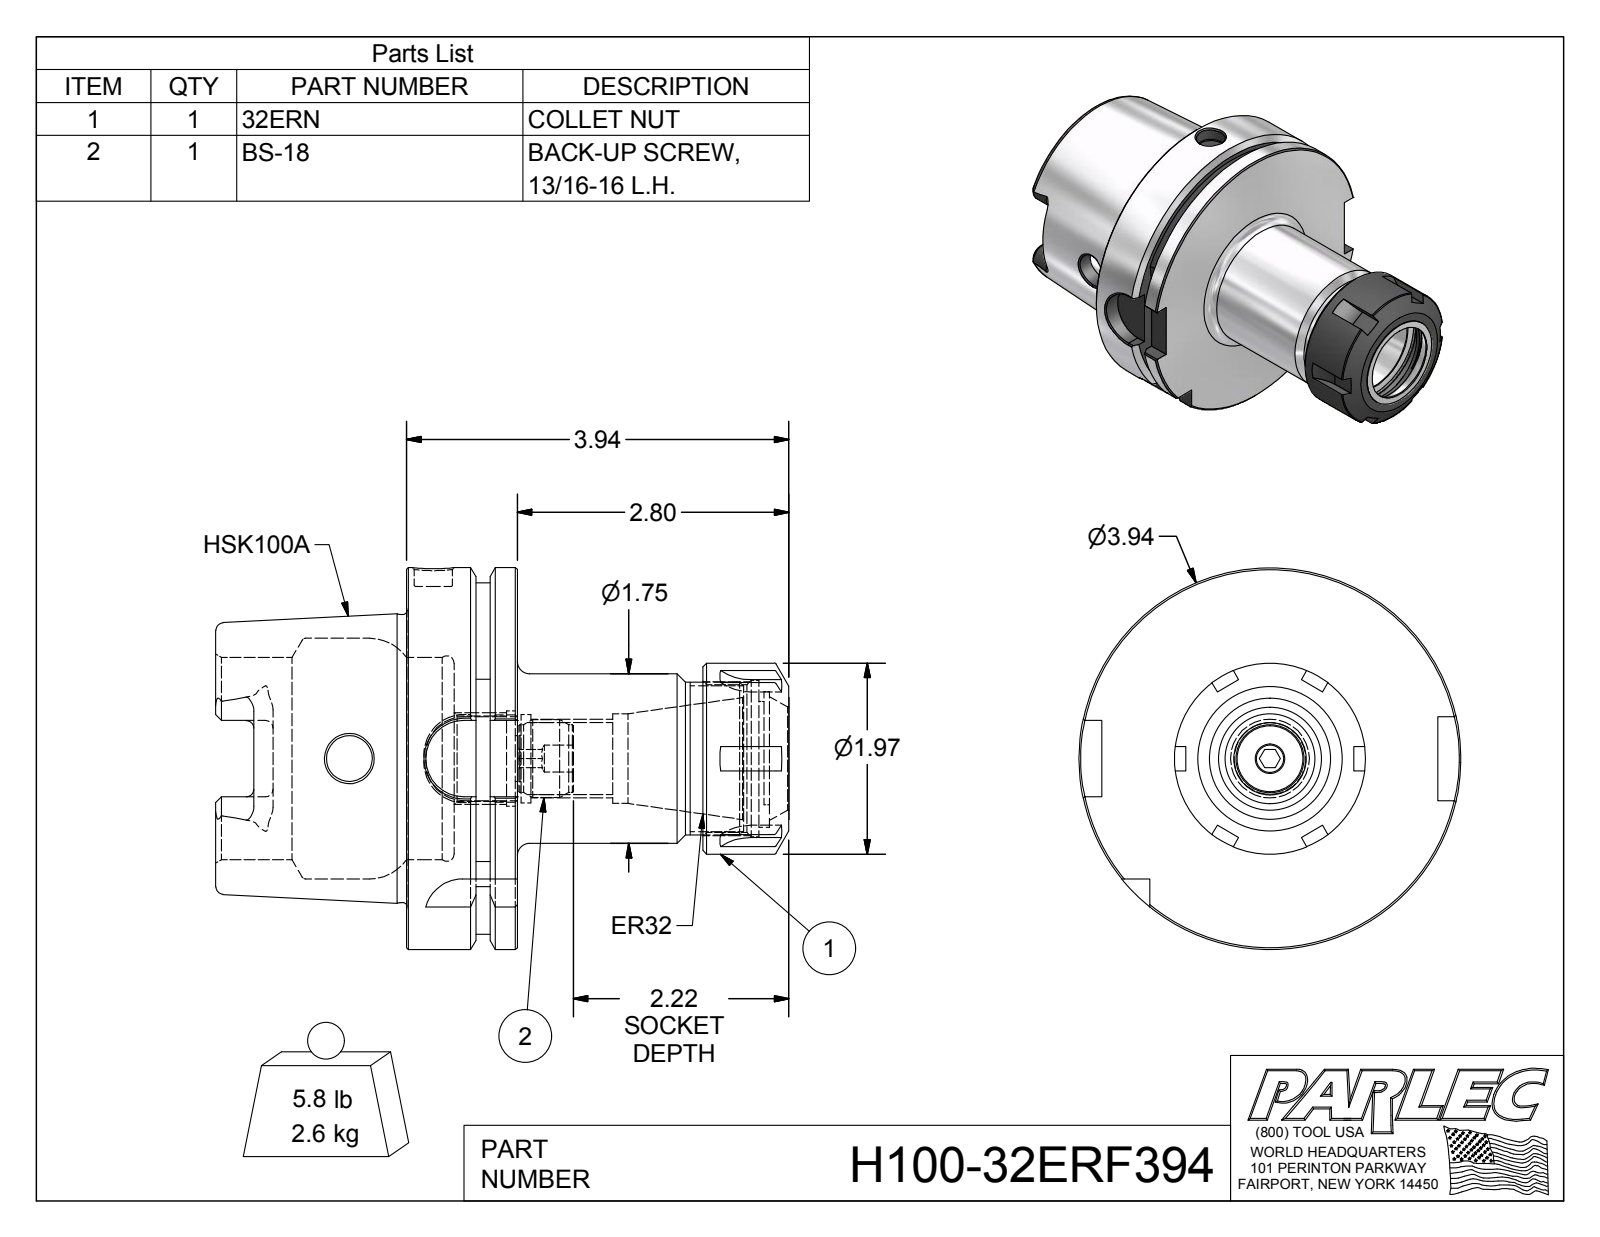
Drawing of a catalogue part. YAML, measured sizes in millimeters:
part_name: "H100-32ER4-1; 32ERN; BS-18; H100-32ERF394"
step_written_by: "Autodesk Inventor 2016 (AUTOMOTIVE_DESIGN)"
units: millimeters
bodies: {solids: 3, faces: 236, planar: 86, cylindrical: 61, other: 89}
overall_size: [150.08, 100, 100]
volume: 335718
surface_area: 72418
round_holes:
  - {diameter: 9, count: 2}
  - {diameter: 12, count: 2}
  - {diameter: 7.11, count: 1}
  - {diameter: 10, count: 1}
  - {diameter: 18.92, count: 1}
  - {diameter: 22.38, count: 1}
  - {diameter: 23.16, count: 1}
  - {diameter: 23.5, count: 1}
  - {diameter: 25.02, count: 1}
  - {diameter: 27, count: 1}
  - {diameter: 33.02, count: 1}
  - {diameter: 38.65, count: 1}
round_bosses_or_shafts:
  - {diameter: 100, count: 1}
  - {diameter: 92, count: 1}
  - {diameter: 75.36, count: 1}
  - {diameter: 50, count: 1}
  - {diameter: 44.45, count: 1}
  - {diameter: 40, count: 1}
  - {diameter: 20.45, count: 1}
  - {diameter: 17.78, count: 1}
partial_cylinders:
  - {radius: 0.51, count: 12}
  - {radius: 2, count: 6}
  - {radius: 4.88, count: 4}
  - {radius: 10, count: 4}
  - {radius: 14.9, count: 1}
  - {radius: 17.5, count: 1}
face_to_face_distances: [29, 12.5, 16.5, 50, 62.5, 79, 150.08, 100.08, 87.58, 71.08]
hole_center_spacings: [1.85]
